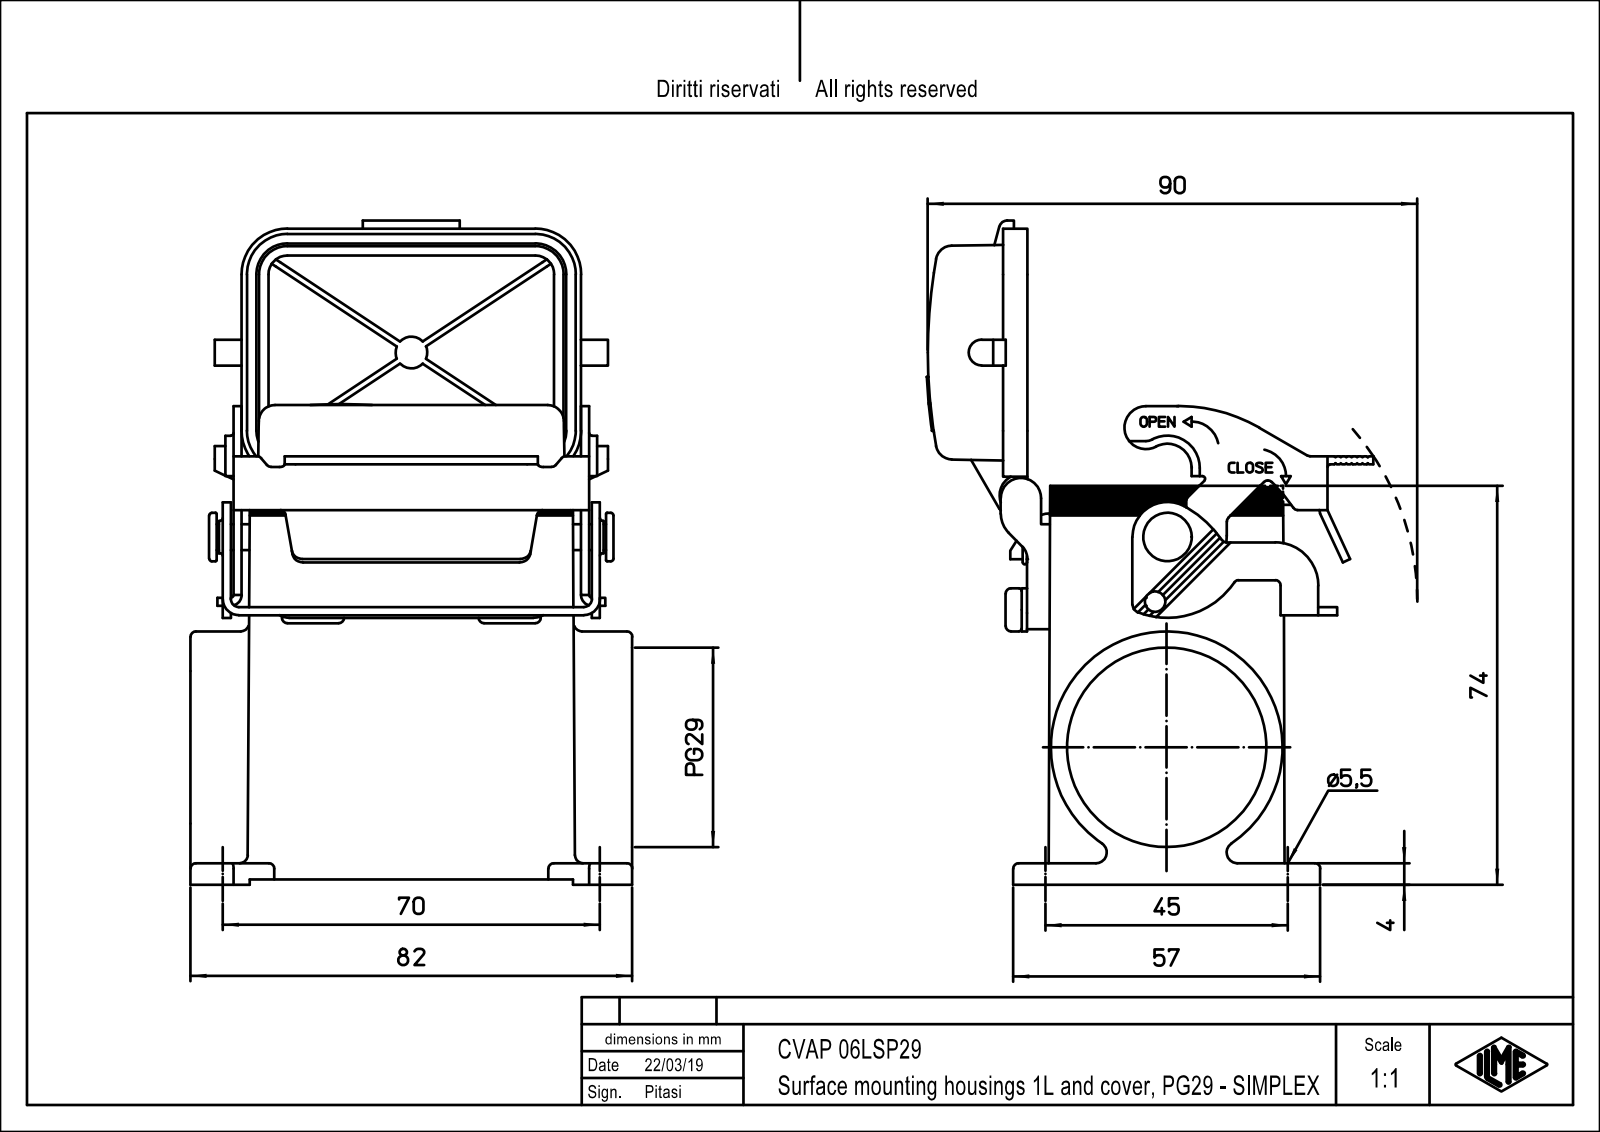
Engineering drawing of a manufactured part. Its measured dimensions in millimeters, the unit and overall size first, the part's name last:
Units: millimetres
Overall size (bounding box): 122.72 × 82 × 79.9
Round holes (diameter × count): ⌀2.46 ×4, ⌀3 ×4, ⌀5.5 ×4, ⌀32 ×1, ⌀37 ×1
Round bosses / shafts (diameter × count): ⌀0.8 ×3, ⌀43 ×1, ⌀9 ×1, ⌀8.4 ×1, ⌀8 ×1, ⌀6 ×1, ⌀2.4 ×1
Partial cylindrical surfaces — rounded edges, fillets, slot ends (radius × count): R2 ×20, R3 ×15, R1.5 ×8, R3.5 ×7, R1 ×5, R6 ×5, R0.5 ×4, R1.8 ×4
Main face-to-face distances: 4, 40.5, 44.5, 1.5, 59.5, 36.5, 9.5, 2, 47.75, 8
Hole centre spacings: 15.81, 38.28, 57.71, 67.42, 27, 44, 45, 51.62
Volume: 110 190 mm³ · Surface area: 62 519 mm²
Bodies: 1 solid, 608 faces (383 planar, 201 cylindrical, 24 other)
Part name (STEP PRODUCT): CVAP_06_LSP29; CVAP_06LSP29.stp
STEP written by: PTC Creo Elements/Direct Modeling 19.0E 27-Jun-2016 (C) Parametric Technology GmbH (AUTOMOTIVE_DESIGN)
